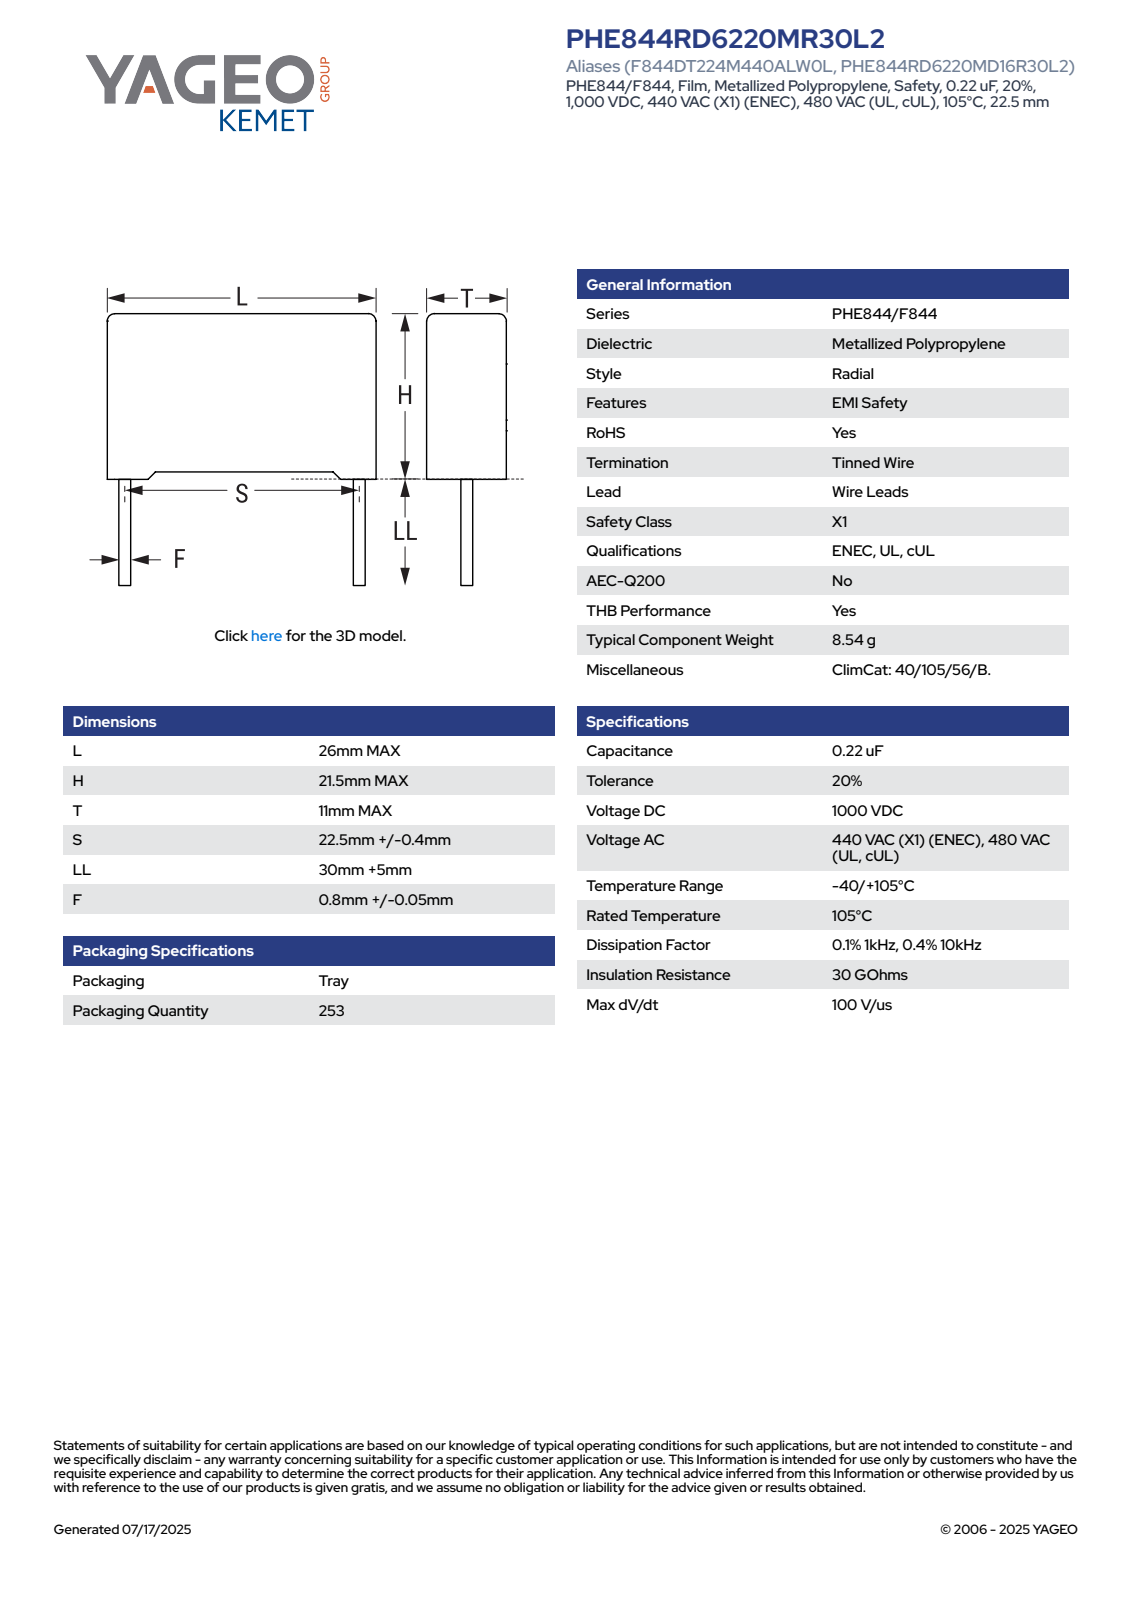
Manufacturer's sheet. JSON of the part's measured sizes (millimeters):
{"part_name": "CFR_RB2_26X21.5X11_L26H21.5T11S22.5LL35F0.85", "step_written_by": "SolidWorks 2021 (AUTOMOTIVE_DESIGN)", "units": "millimeters", "bodies": {"solids": 4, "faces": 85, "planar": 77, "cylindrical": 8, "other": 0}, "overall_size": [56.5, 26, 11.01], "volume_mm3": 5993, "surface_area_mm2": 2384, "round_bosses_or_shafts": [[0.85, 2]], "partial_cylinders_radius": [[0.5, 4]], "face_to_face_distances": [11, 26, 20.75, 20.76, 0.74, 0.75, 21.5, 0.87, 25.13, 10.13]}
